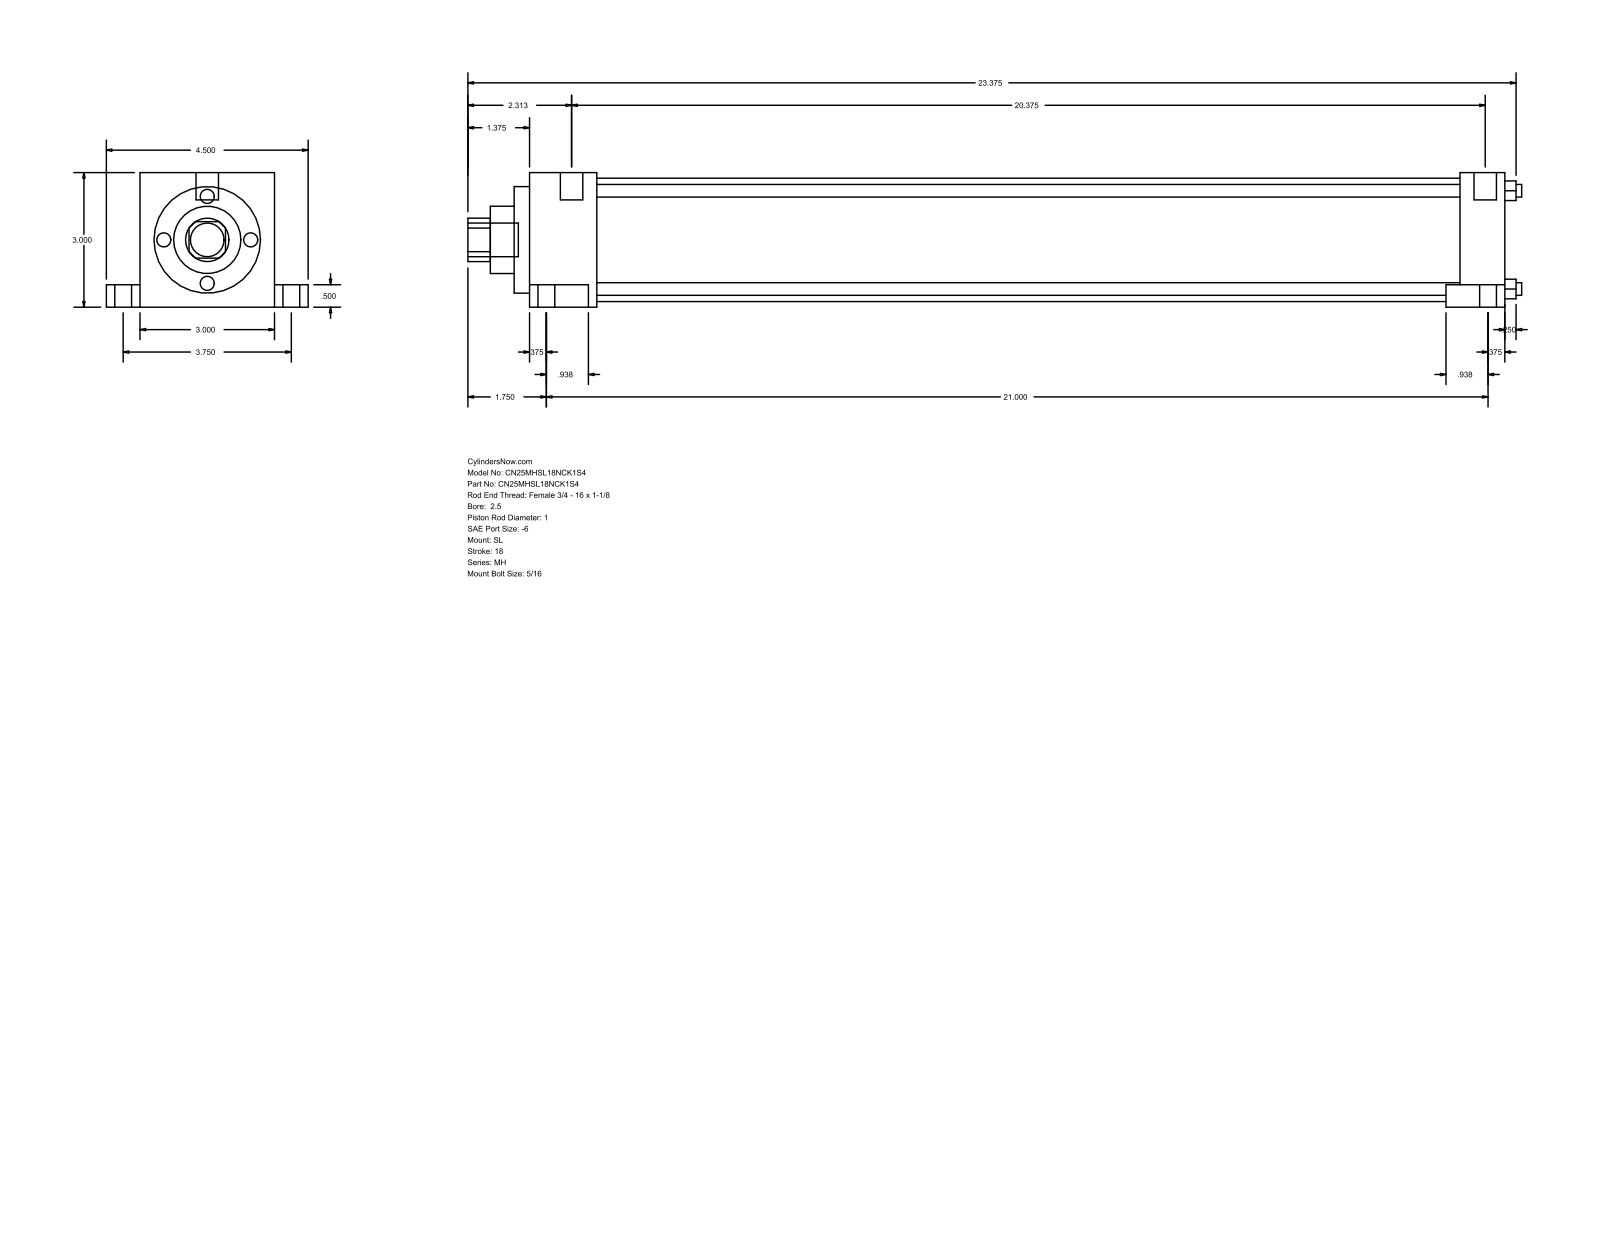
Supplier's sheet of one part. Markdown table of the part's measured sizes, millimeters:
| quantity | value |
| --- | --- |
| part name | MH_SL__0250_1 |
| STEP written by | GSSL Pune (CONFIG_CONTROL_DESIGN) |
| units | millimeters |
| bodies | 0 solids, 86 faces (61 planar, 25 cylindrical, 0 other) |
| overall size | 596.9 × 114.3 × 76.2 |
| round holes (diameter × count) | 7.14 × 4, 25.4 × 1, 38.1 × 1, 60.33 × 1, 69.85 × 1 |
| round bosses / shafts (diameter × count) | 15.88 × 2, 9.53 × 2, 5.56 × 2, 19.05 × 1, 12.7 × 1 |
| partial cylindrical surfaces (radius × count) | 12.29 × 1 |
| main face-to-face distances | 76.2, 25.4, 535.79, 561.19, 12.7, 63.5, 19.05, 95.25, 13.49, 549.28 |
| hole center spacings | 39.33, 55.62, 78.66 |
